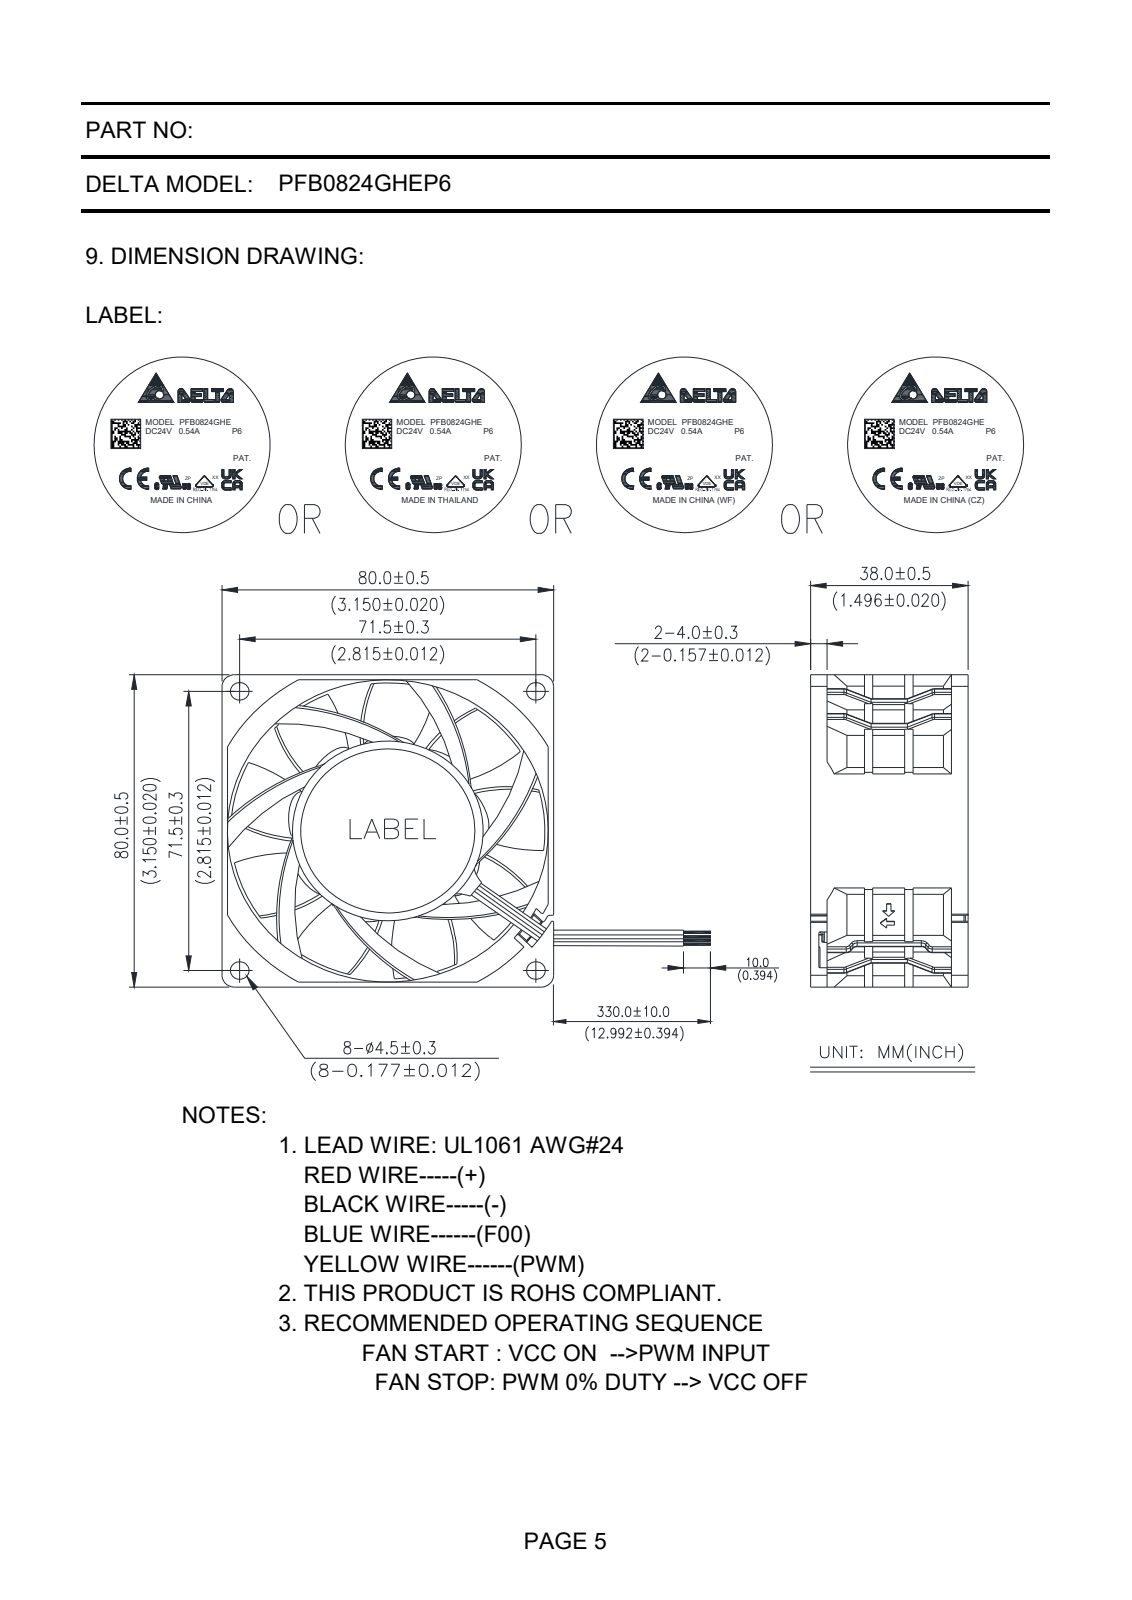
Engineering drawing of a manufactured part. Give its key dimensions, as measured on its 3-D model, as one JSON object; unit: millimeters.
{"part_name": "PRT0034_1_1; PRT0035_1_1; ASM0009_ASM_1_1_ASM; PFB838_ASM", "step_written_by": "CREO PARAMETRIC BY PTC INC, 2020454 (AUTOMOTIVE_DESIGN)", "units": "millimeters", "bodies": {"solids": 2, "faces": 632, "planar": 245, "cylindrical": 238, "other": 149}, "overall_size": [104.03, 102.3, 42.94], "volume_mm3": 90470, "surface_area_mm2": 47736, "round_holes": [[4.5, 4], [77.4, 1]], "round_bosses_or_shafts": [[46, 2]], "partial_cylinders_radius": [[0.4, 68], [0.3, 19], [1.2, 17], [6.34, 8], [3, 4], [44, 2], [45.8, 2], [6.35, 1]], "face_to_face_distances": [12, 2.9, 14.9, 80.03, 79.99, 36.51, 24.51, 21.61, 2, 78.68], "hole_center_spacings": [71.49, 71.5, 101.11, 50.52, 50.54, 50.57, 50.59]}
